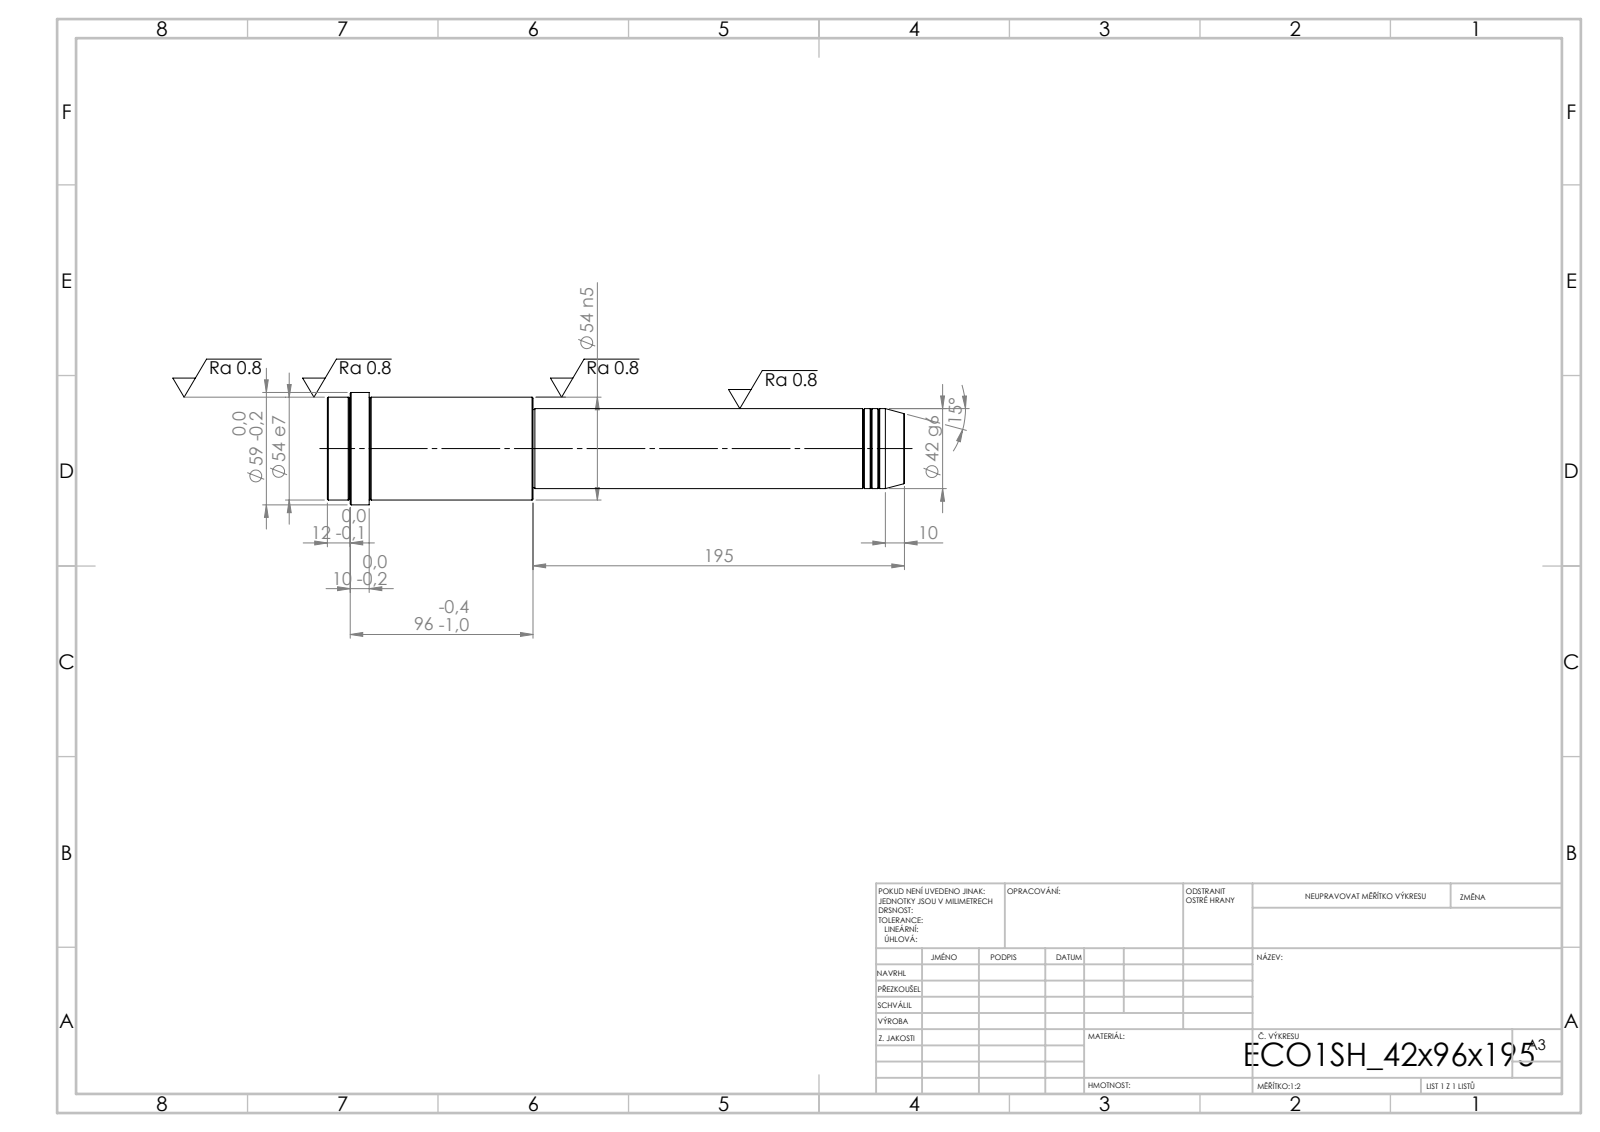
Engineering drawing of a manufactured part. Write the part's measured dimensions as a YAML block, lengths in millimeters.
step_written_by: "SolidWorks 2019 (CONFIG_CONTROL_DESIGN)"
units: millimeters
bodies: {solids: 1, faces: 52, planar: 6, cylindrical: 16, other: 30}
overall_size: [303, 59, 59]
volume: 519830
surface_area: 49668
round_bosses_or_shafts:
  - {diameter: 59, count: 1}
  - {diameter: 54, count: 1}
  - {diameter: 42, count: 1}
  - {diameter: 41, count: 1}
face_to_face_distances: [303, 195, 108, 281, 86, 22, 291, 96, 10, 12]
